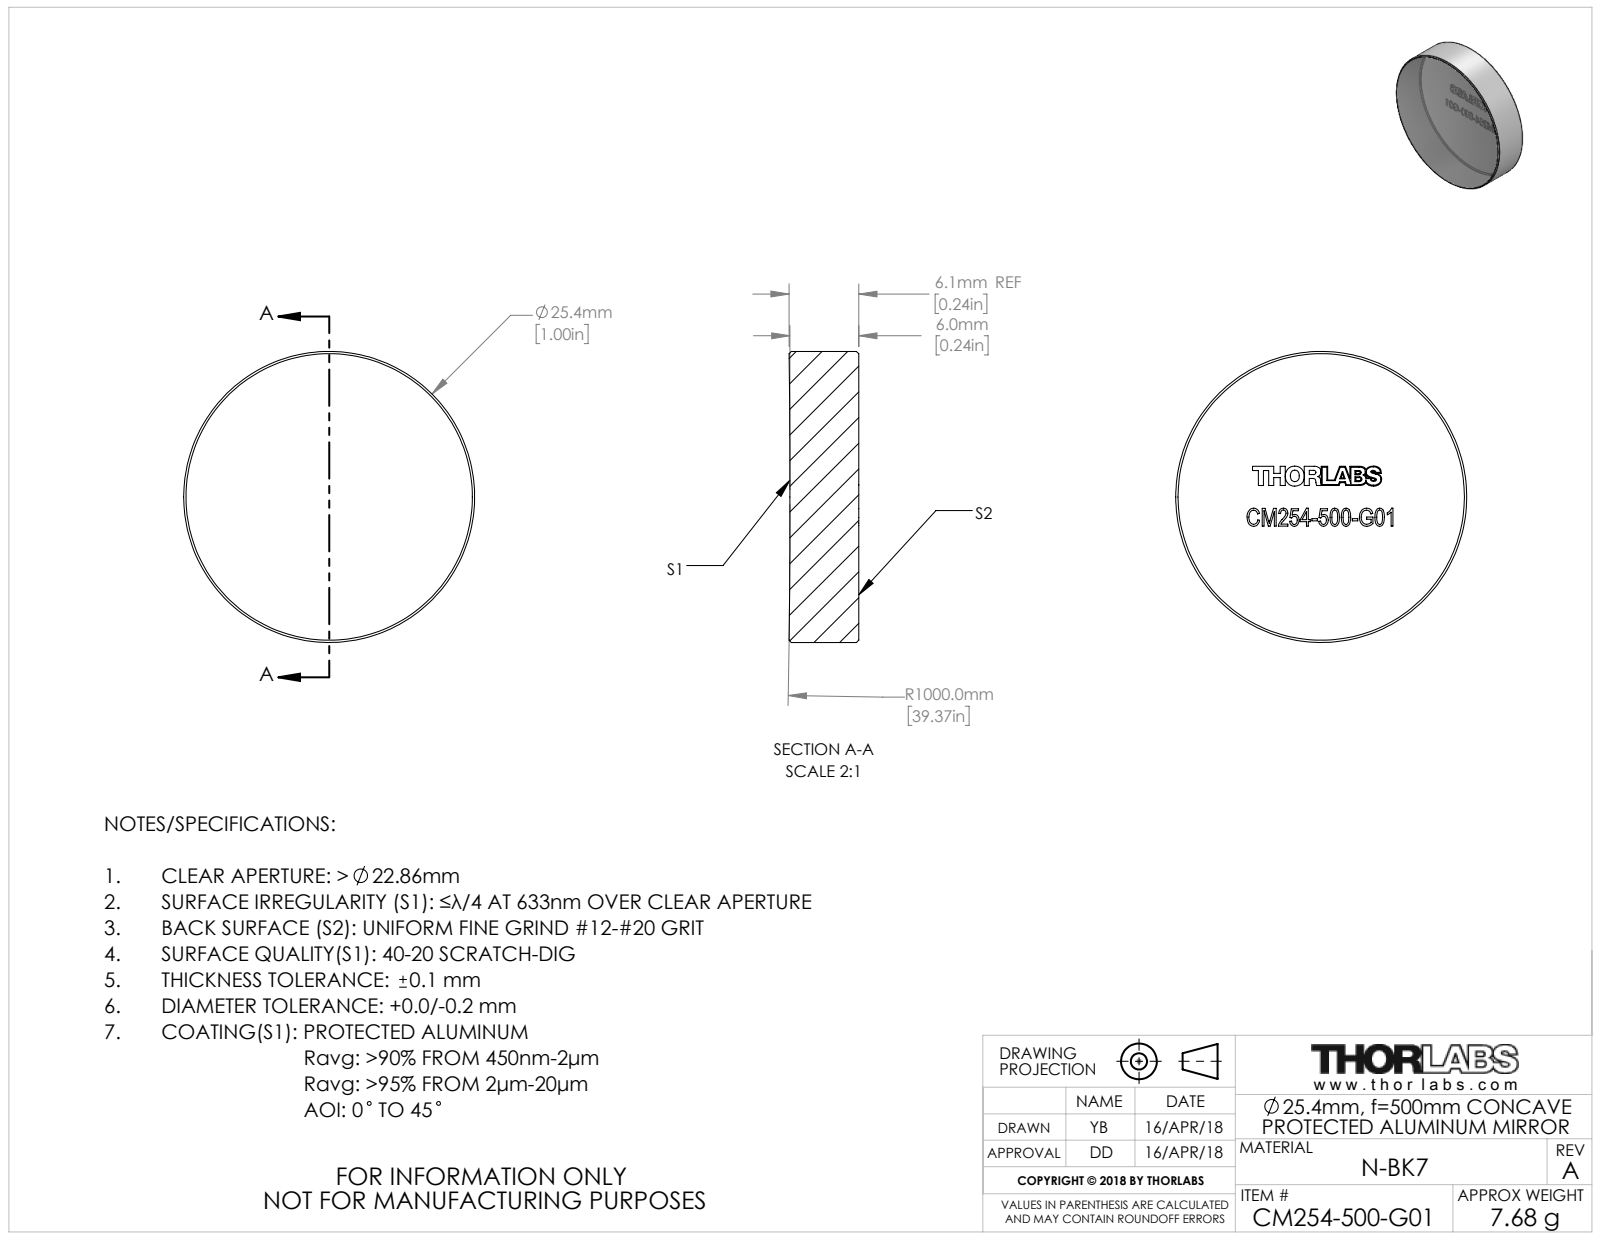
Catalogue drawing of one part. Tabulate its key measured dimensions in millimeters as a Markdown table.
| quantity | value |
| --- | --- |
| part name | TTN153302-E0W |
| STEP written by | SolidWorks 2018 (CONFIG_CONTROL_DESIGN) |
| units | millimeters |
| bodies | 1 solid, 41 faces (33 planar, 2 cylindrical, 6 other) |
| overall size | 25.4 × 25.4 × 6.08 |
| volume | 3 058 mm³ |
| surface area | 1 480 mm² |
| round bosses / shafts (diameter × count) | 25.4 × 1 |
